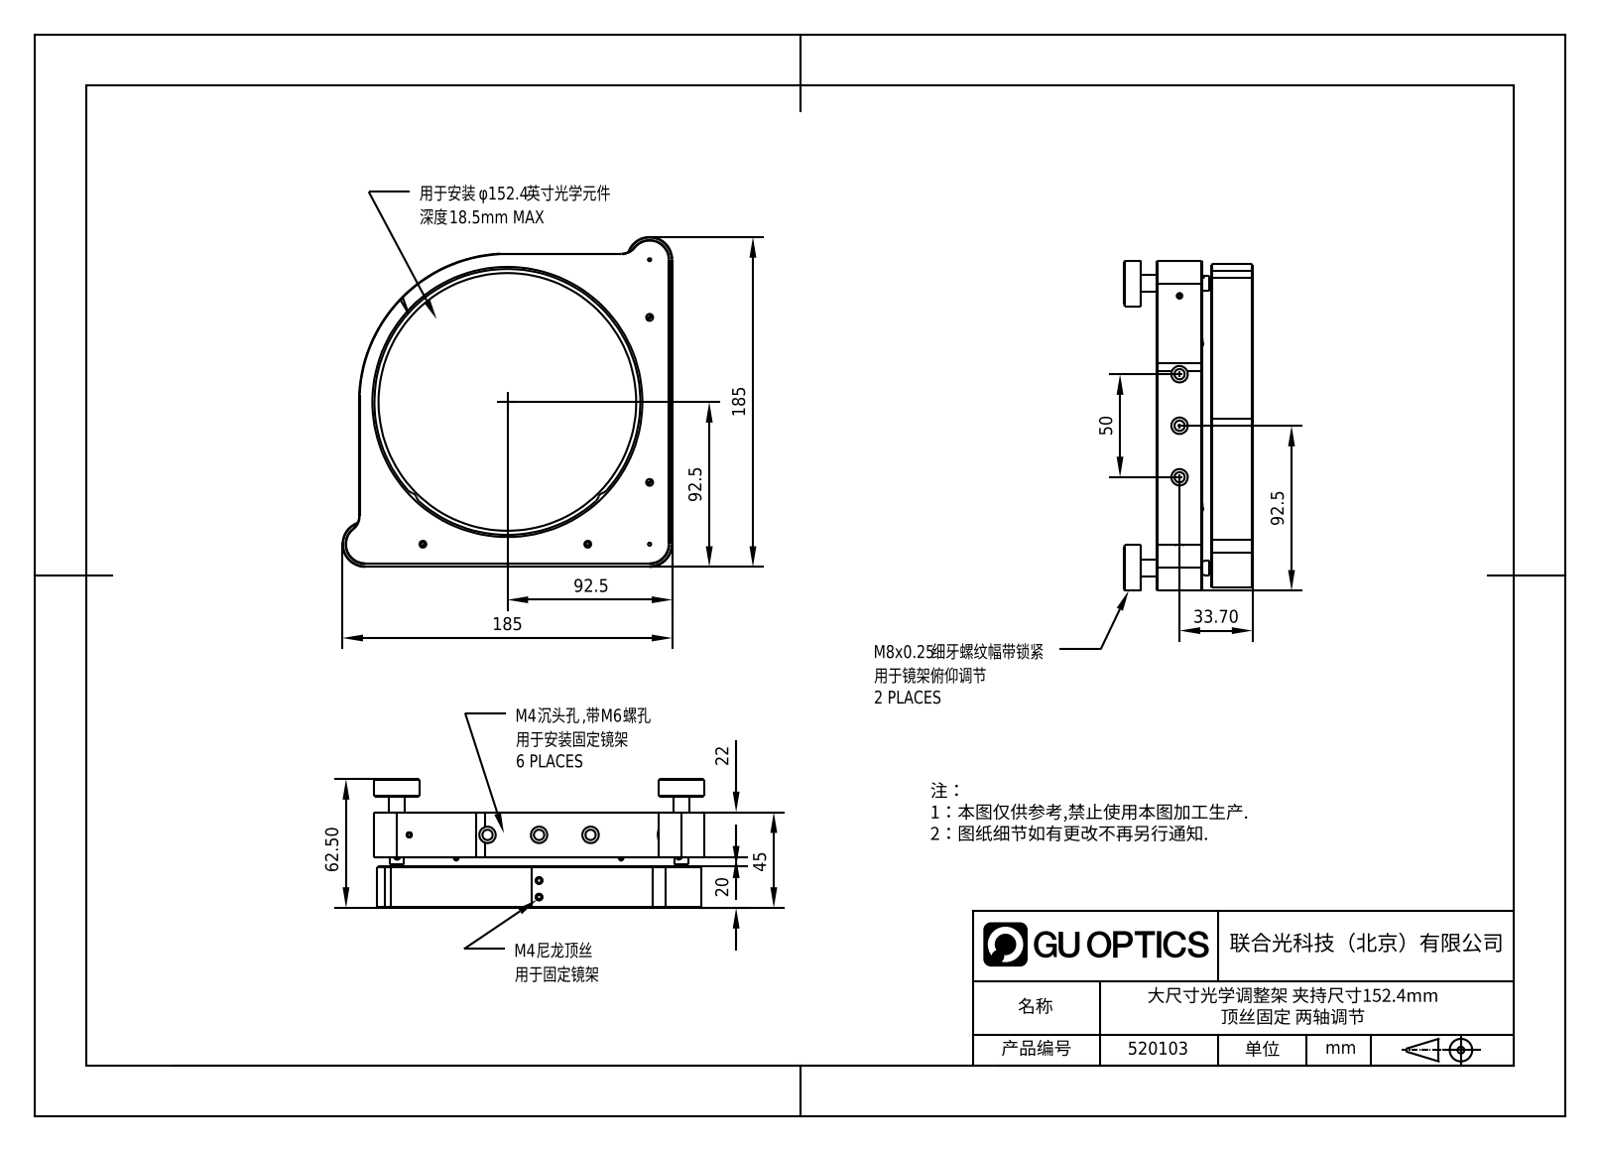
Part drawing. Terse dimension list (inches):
name: 1.1.1.41_ZJB-6.0-2
written by: SolidWorks 2021 (CONFIG_CONTROL_DESIGN)
unit: in
bodies: 0 solids, 386 faces (109 planar, 193 cylindrical, 84 other)
size: 7.283 × 7.283 × 2.461
holes: 12× ⌀0.315, 10× ⌀0.13, 6× ⌀0.197, 3× ⌀0.472, 2× ⌀0.059, 2× ⌀0.098, 2× ⌀0.236, 1× ⌀0.047, 1× ⌀5.921, 1× ⌀6.079
bosses: 6× ⌀0.079, 2× ⌀0.866, 2× ⌀0.315, 2× ⌀0.118, 1× ⌀0.512, 1× ⌀0.5, 1× ⌀0.157
rounds: 12× R0.041, 9× R0.118, 5× R0.197, 4× R0.236, 3× R0.098, 3× R0.374, 2× R0.984, 2× R1.102
face distances: 0.866, 0.787, 0.154, 0.941, 1.02, 1.807, 0.059, 0.63, 0.591, 0.65
hole spacings: 0.984, 1.302, 1.527, 4.538, 0.315, 0.846, 0.853, 1.168
